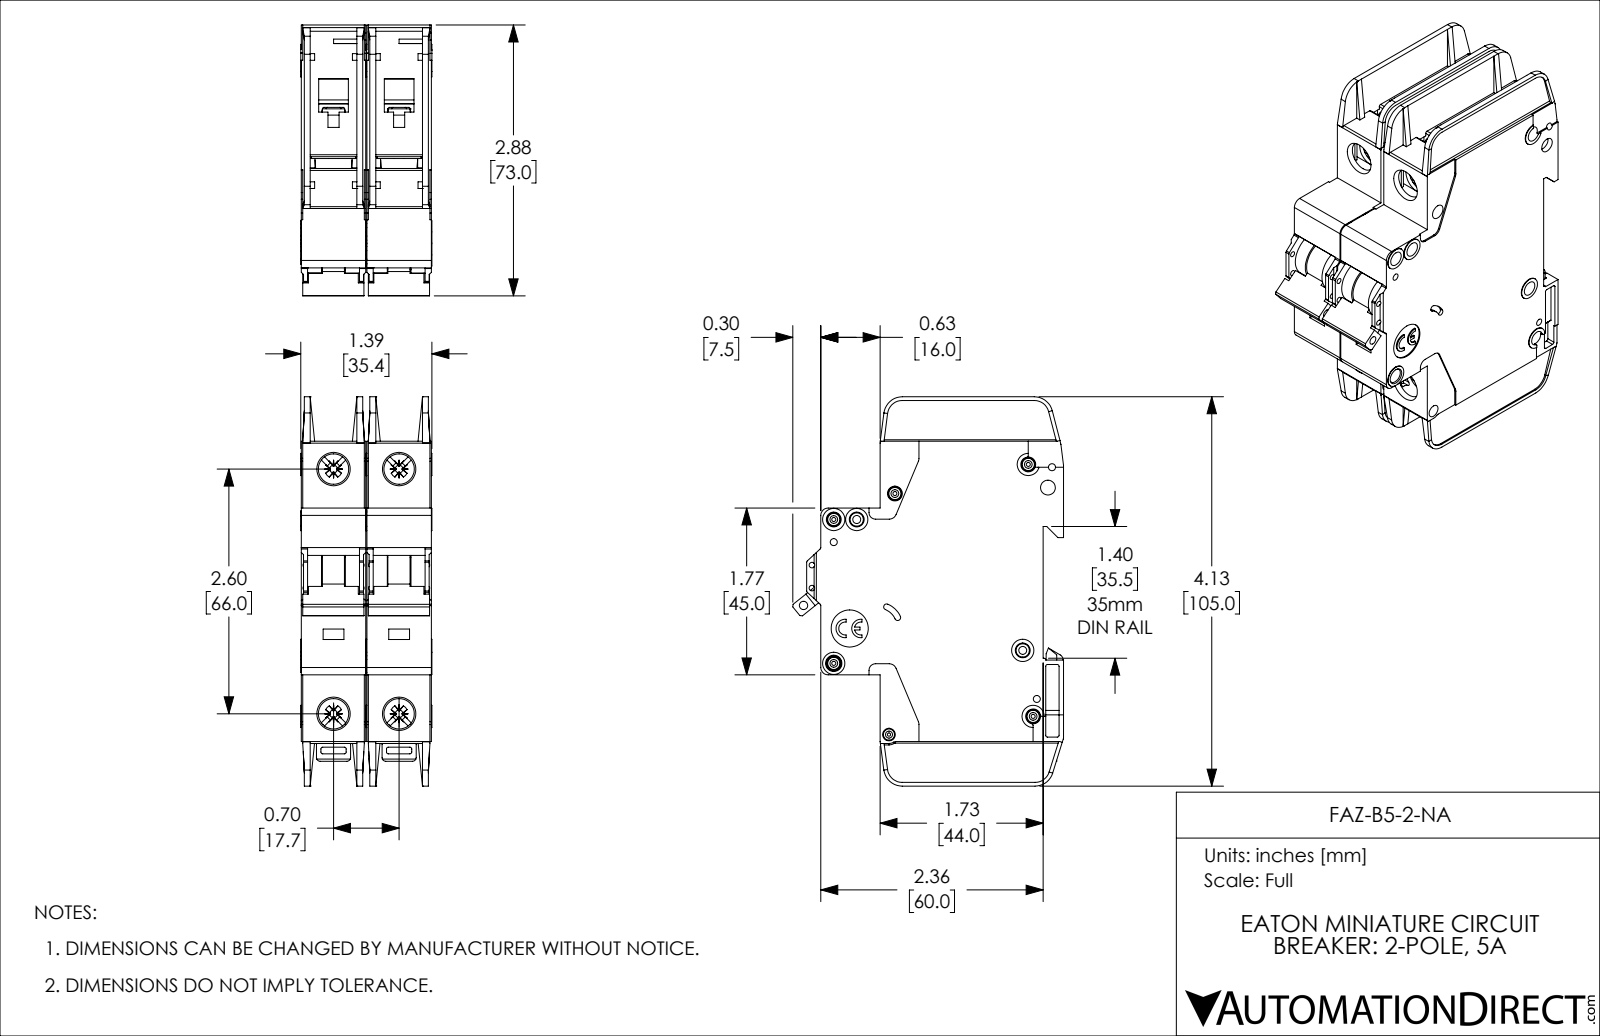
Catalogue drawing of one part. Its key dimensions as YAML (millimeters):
part_name: "FAZ-B5-2-NA"
step_written_by: "SolidWorks 2019 (AUTOMOTIVE_DESIGN)"
units: millimeters
bodies: {solids: 2, faces: 2254, planar: 1342, cylindrical: 714, other: 198}
overall_size: [105, 73.1, 35.4]
volume: 153500
surface_area: 52910
round_holes:
  - {diameter: 4, count: 8}
  - {diameter: 1.1, count: 5}
  - {diameter: 1.9, count: 4}
  - {diameter: 8.2, count: 4}
  - {diameter: 1.5, count: 2}
  - {diameter: 2.2, count: 2}
  - {diameter: 0.9, count: 1}
  - {diameter: 2.3, count: 1}
  - {diameter: 2.5, count: 1}
  - {diameter: 3.4, count: 1}
  - {diameter: 10, count: 1}
round_bosses_or_shafts:
  - {diameter: 3.3, count: 5}
  - {diameter: 6, count: 4}
  - {diameter: 3, count: 3}
  - {diameter: 2.5, count: 2}
partial_cylinders:
  - {radius: 0.5, count: 57}
  - {radius: 0.4, count: 20}
  - {radius: 1, count: 14}
  - {radius: 2, count: 10}
  - {radius: 1.1, count: 8}
  - {radius: 0.2, count: 5}
  - {radius: 5, count: 5}
  - {radius: 0.3, count: 4}
face_to_face_distances: [17.7, 1.2, 17.4, 15, 2.4, 16.2, 13.8, 35.1, 18.9, 16.5]
hole_center_spacings: [6.2, 13.6, 17.7, 22.1, 66, 68.3, 4.8, 5.1]
